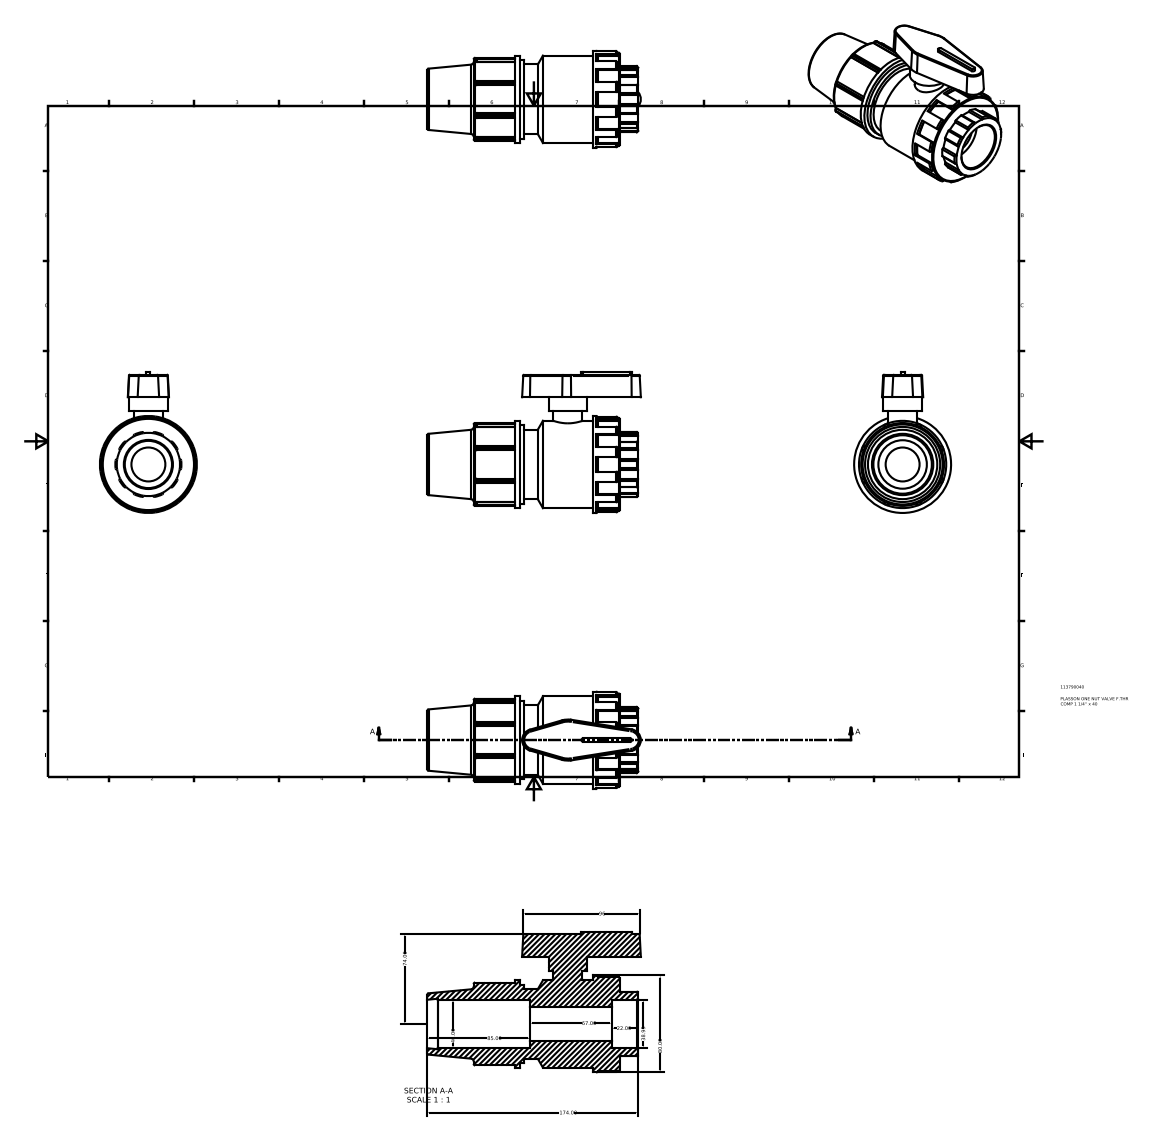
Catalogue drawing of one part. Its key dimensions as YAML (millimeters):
part_name: "113790040"
step_written_by: "Autodesk Inventor 2015 (AUTOMOTIVE_DESIGN)"
units: millimeters
bodies: {solids: 1, faces: 248, planar: 99, cylindrical: 74, other: 75}
overall_size: [176.17, 116.22, 80]
volume: 474899
surface_area: 76277
round_holes:
  - {diameter: 28, count: 1}
  - {diameter: 38.95, count: 1}
  - {diameter: 40, count: 1}
round_bosses_or_shafts:
  - {diameter: 80, count: 1}
  - {diameter: 76.8, count: 1}
  - {diameter: 72, count: 1}
  - {diameter: 68.4, count: 1}
  - {diameter: 64.8, count: 1}
  - {diameter: 57.6, count: 1}
  - {diameter: 32, count: 1}
  - {diameter: 24, count: 1}
partial_cylinders:
  - {radius: 1.17, count: 20}
  - {radius: 1.2, count: 16}
  - {radius: 0.78, count: 4}
  - {radius: 1.6, count: 2}
  - {radius: 26.1, count: 1}
  - {radius: 27.27, count: 1}
face_to_face_distances: [18.5, 22, 15.4, 37.4, 38.25, 60.1, 82.1, 97.5, 3.6, 56.5]
